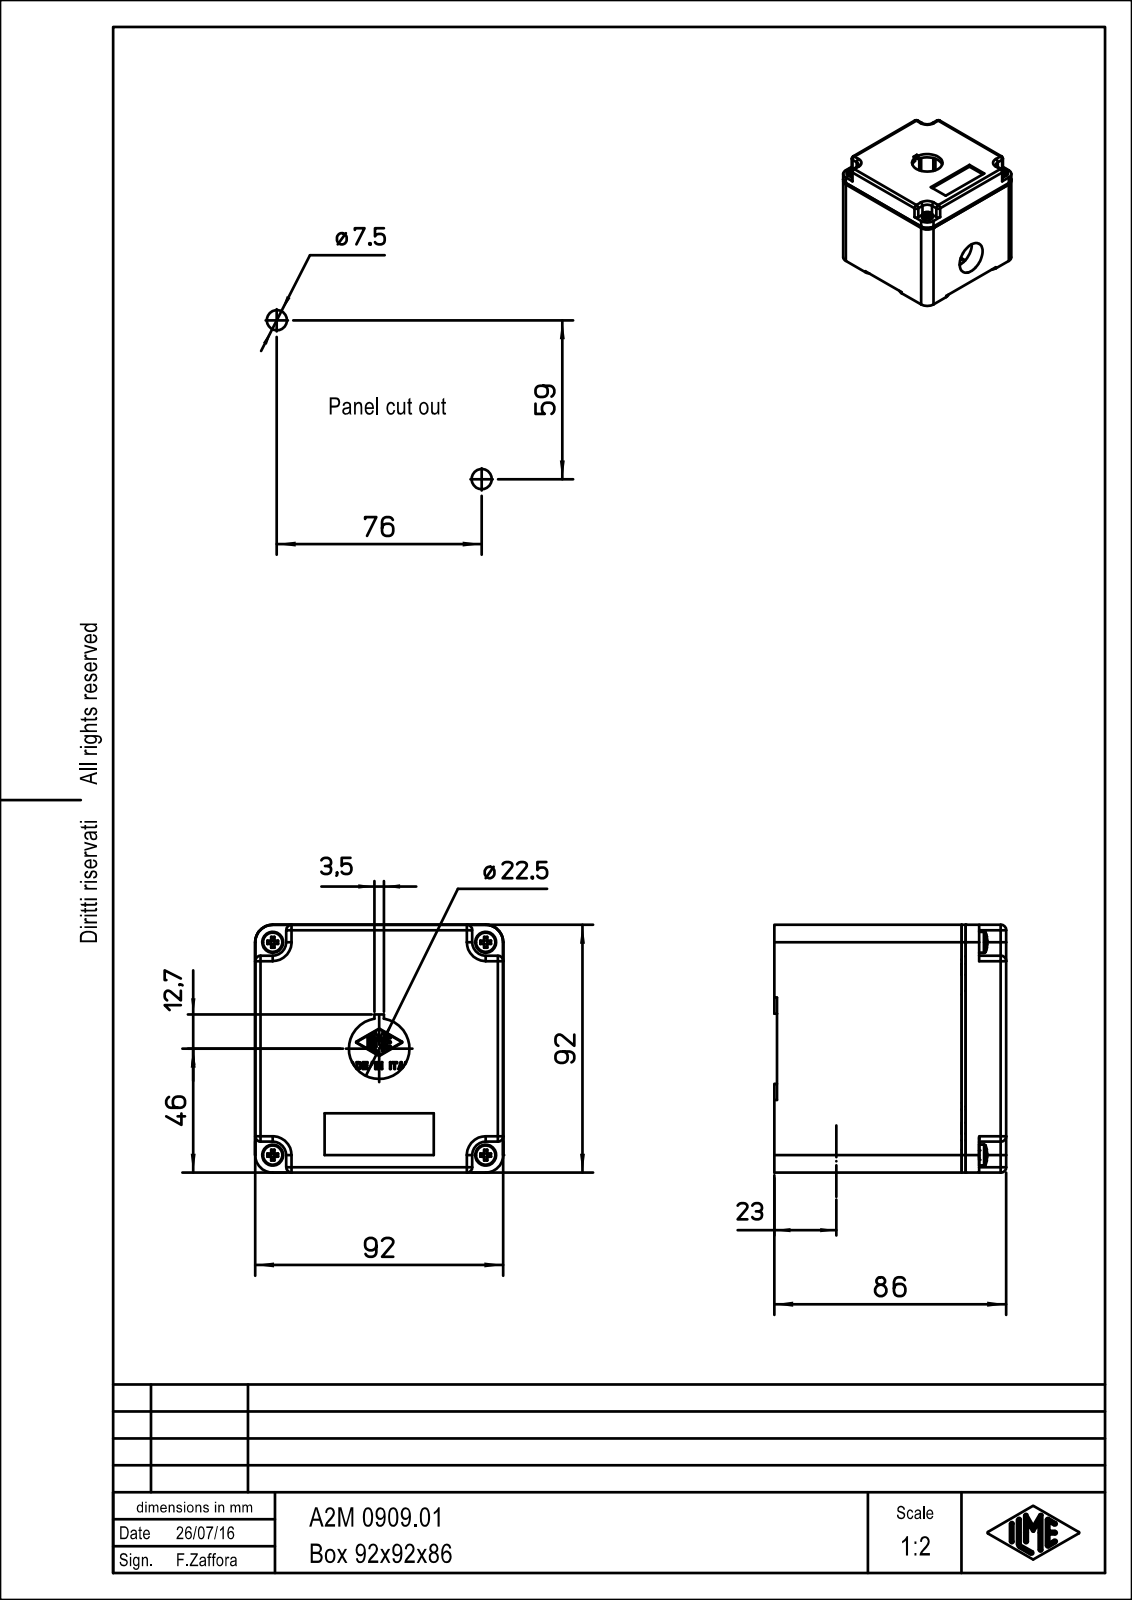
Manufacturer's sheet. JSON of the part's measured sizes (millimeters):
{"part_name": "COVER; BOX; A2M_0909.01", "step_written_by": "PTC Creo Elements/Direct Modeling 19.0B 21-Mar-2015 (C) Parametric Technology GmbH (AUTOMOTIVE_DESIGN)", "units": "millimeters", "bodies": {"solids": 2, "faces": 1019, "planar": 790, "cylindrical": 186, "other": 43}, "overall_size": [92.02, 92, 86], "volume_mm3": 216252, "surface_area_mm2": 103480, "round_holes": [[3.3, 6], [4.5, 4], [5.8, 2], [7.5, 2], [10.6, 2], [22.5, 1], [23.4, 1]], "round_bosses_or_shafts": [[7.8, 4], [4, 4], [6.2, 2], [6, 2], [7, 1]], "partial_cylinders_radius": [[0.33, 22], [2, 17], [6, 12], [6.5, 12], [5, 6], [8, 6], [0.27, 4], [0.27, 4]], "face_to_face_distances": [3, 92, 82, 4.38, 87.63, 87.62, 4.37, 83.25, 13.5, 65.5], "hole_center_spacings": [79, 111.72, 55.86, 78.14, 103.77, 10.11, 11.67, 11.77]}
